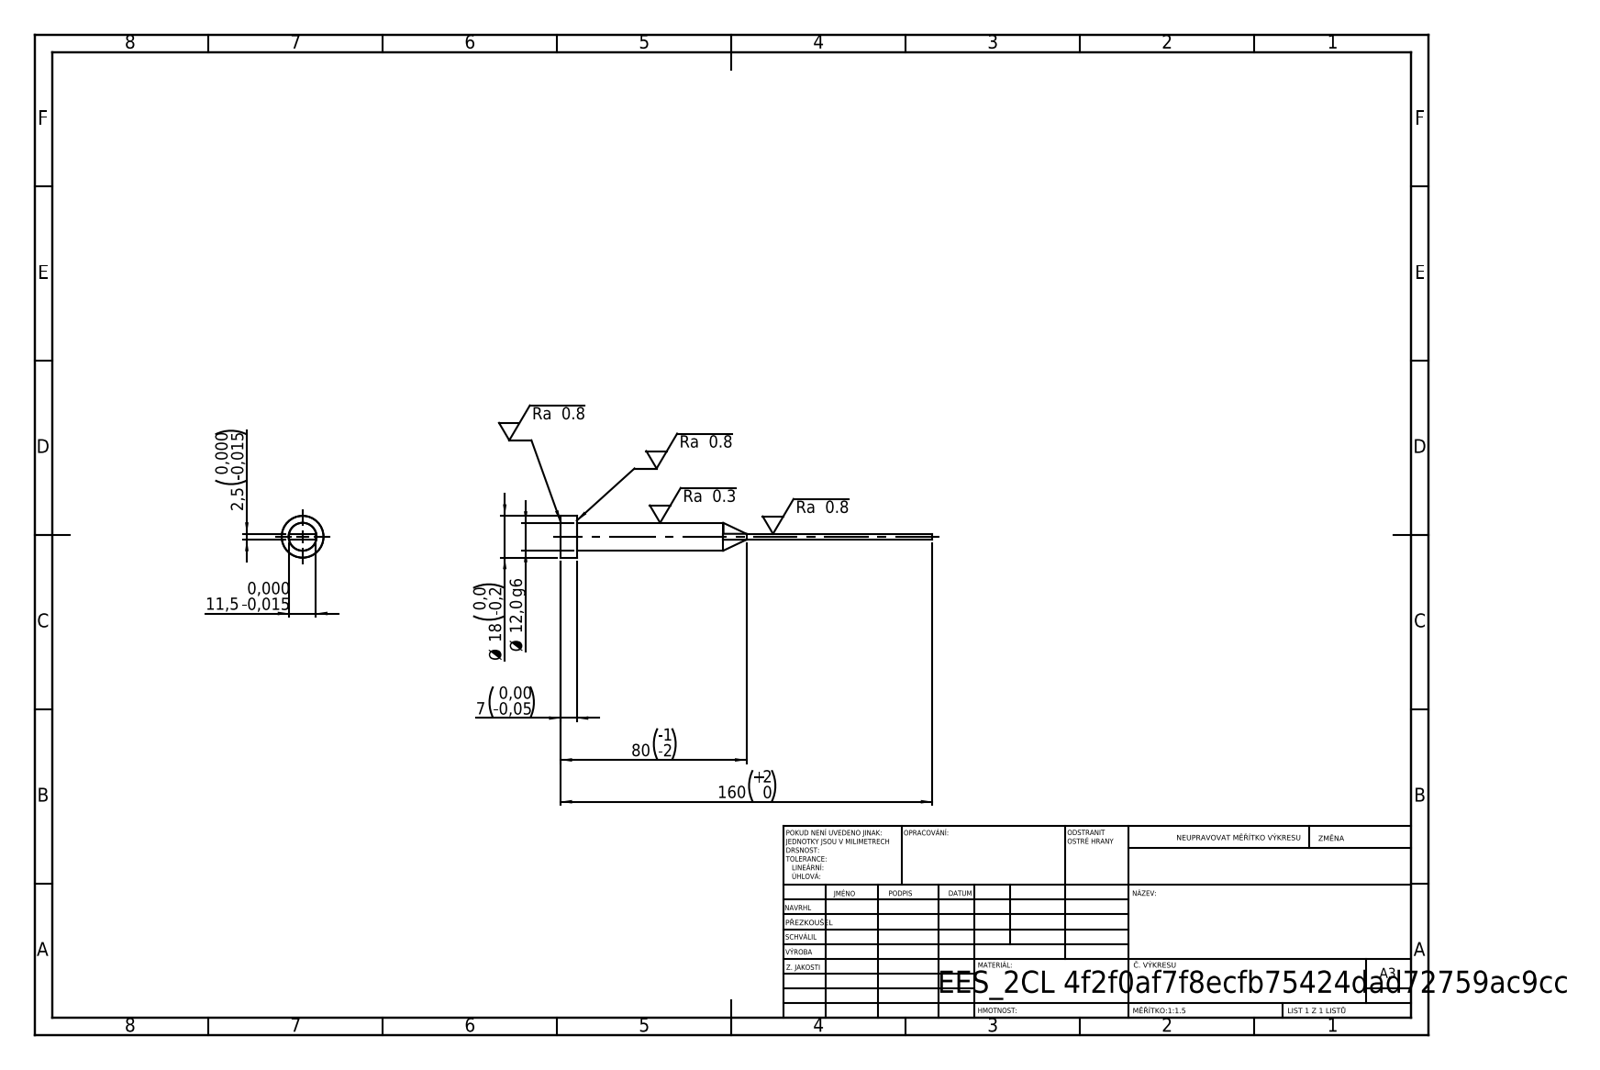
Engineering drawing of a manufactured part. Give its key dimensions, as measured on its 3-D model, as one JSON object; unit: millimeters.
{"step_written_by": "SolidWorks 2019 (CONFIG_CONTROL_DESIGN)", "units": "millimeters", "bodies": {"solids": 1, "faces": 15, "planar": 7, "cylindrical": 4, "other": 4}, "overall_size": [160, 18, 18], "volume_mm3": 11886, "surface_area_mm2": 5765, "round_bosses_or_shafts": [[18, 1], [12, 1]], "face_to_face_distances": [2.5, 11.5, 7, 160, 153]}
